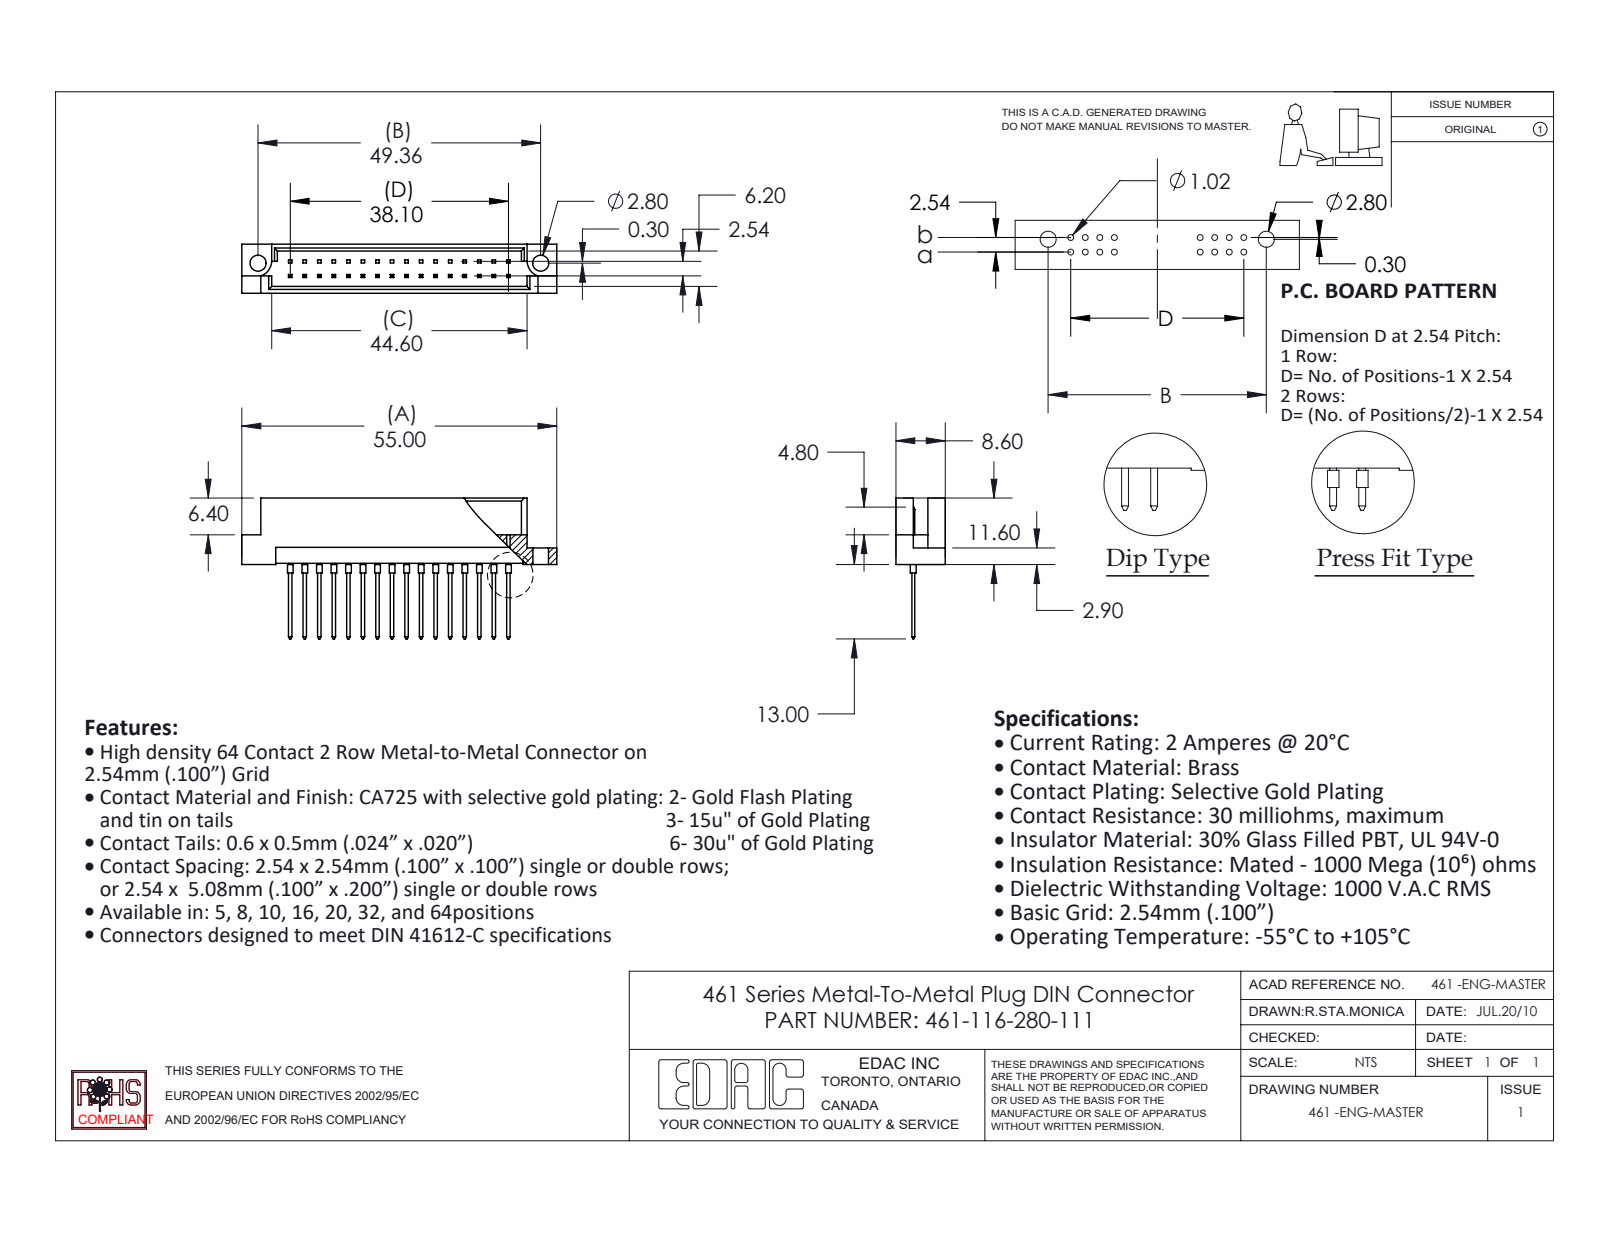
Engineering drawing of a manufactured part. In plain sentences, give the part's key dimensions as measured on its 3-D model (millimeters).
The part is named "461-290_80; 461 Part_32; 461-116-280-111". Its 3-D file was written by "SolidWorks 2020 (CONFIG_CONTROL_DESIGN)". It is 17 solids with 528 faces: 490 planar, 38 cylindrical and 0 other. Overall it measures 55 by 24.6 by 8.6 millimeters. Its volume is 2 774 cubic millimeters and its surface area 4 089 square millimeters. Round holes: 2 of diameter 2.8. Round bosses or shafts: 16 of diameter 1. Partial cylindrical surfaces (rounded edges, fillets, slot ends): 2 of radius 2.8. The main face-to-face distances are 1.2, 7.4, 8.6, 6.2, 2.54, 2.78, 5.82, 1.58, 4.62, 3.28. The hole center spacings are 49.36.
